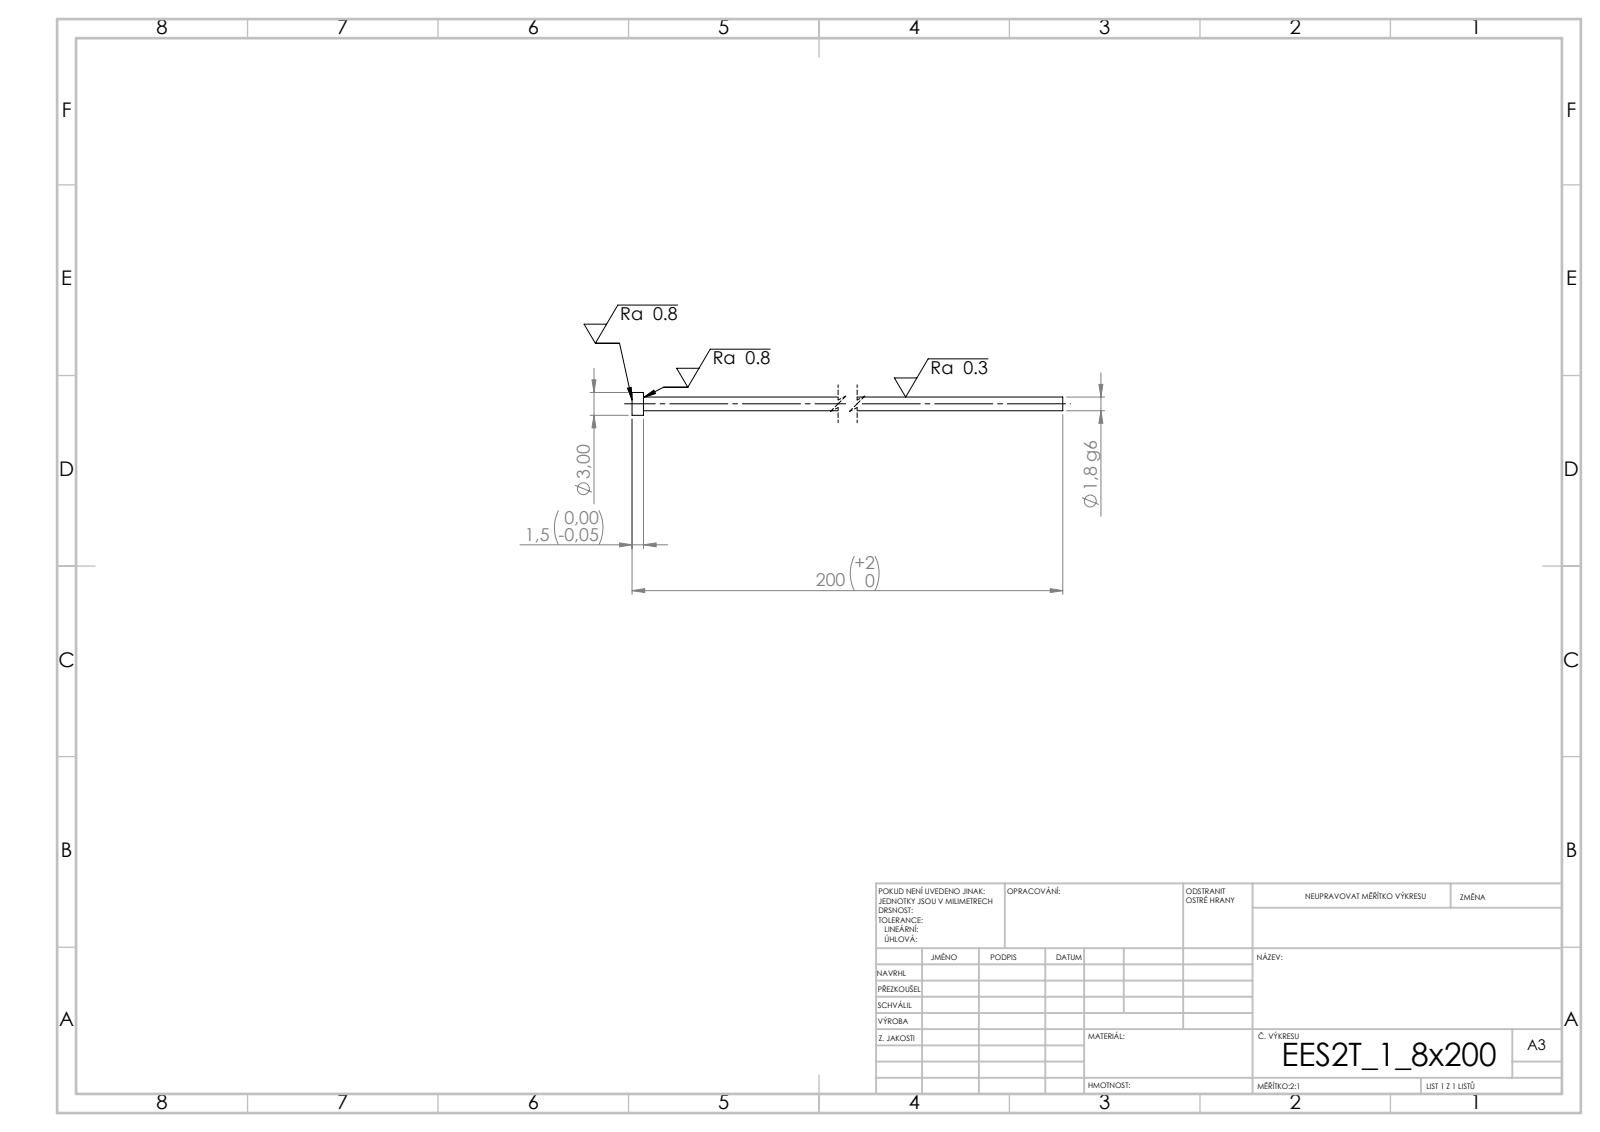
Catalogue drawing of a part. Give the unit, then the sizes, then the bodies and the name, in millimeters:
Units: millimetres
Overall size (bounding box): 200 × 3 × 3
Round bosses / shafts (diameter × count): ⌀3 ×1, ⌀1.8 ×1
Main face-to-face distances: 1.5, 200, 198.5
Volume: 516 mm³ · Surface area: 1 151 mm²
Bodies: 1 solid, 7 faces (3 planar, 4 cylindrical, 0 other)
STEP written by: SolidWorks 2019 (CONFIG_CONTROL_DESIGN)
